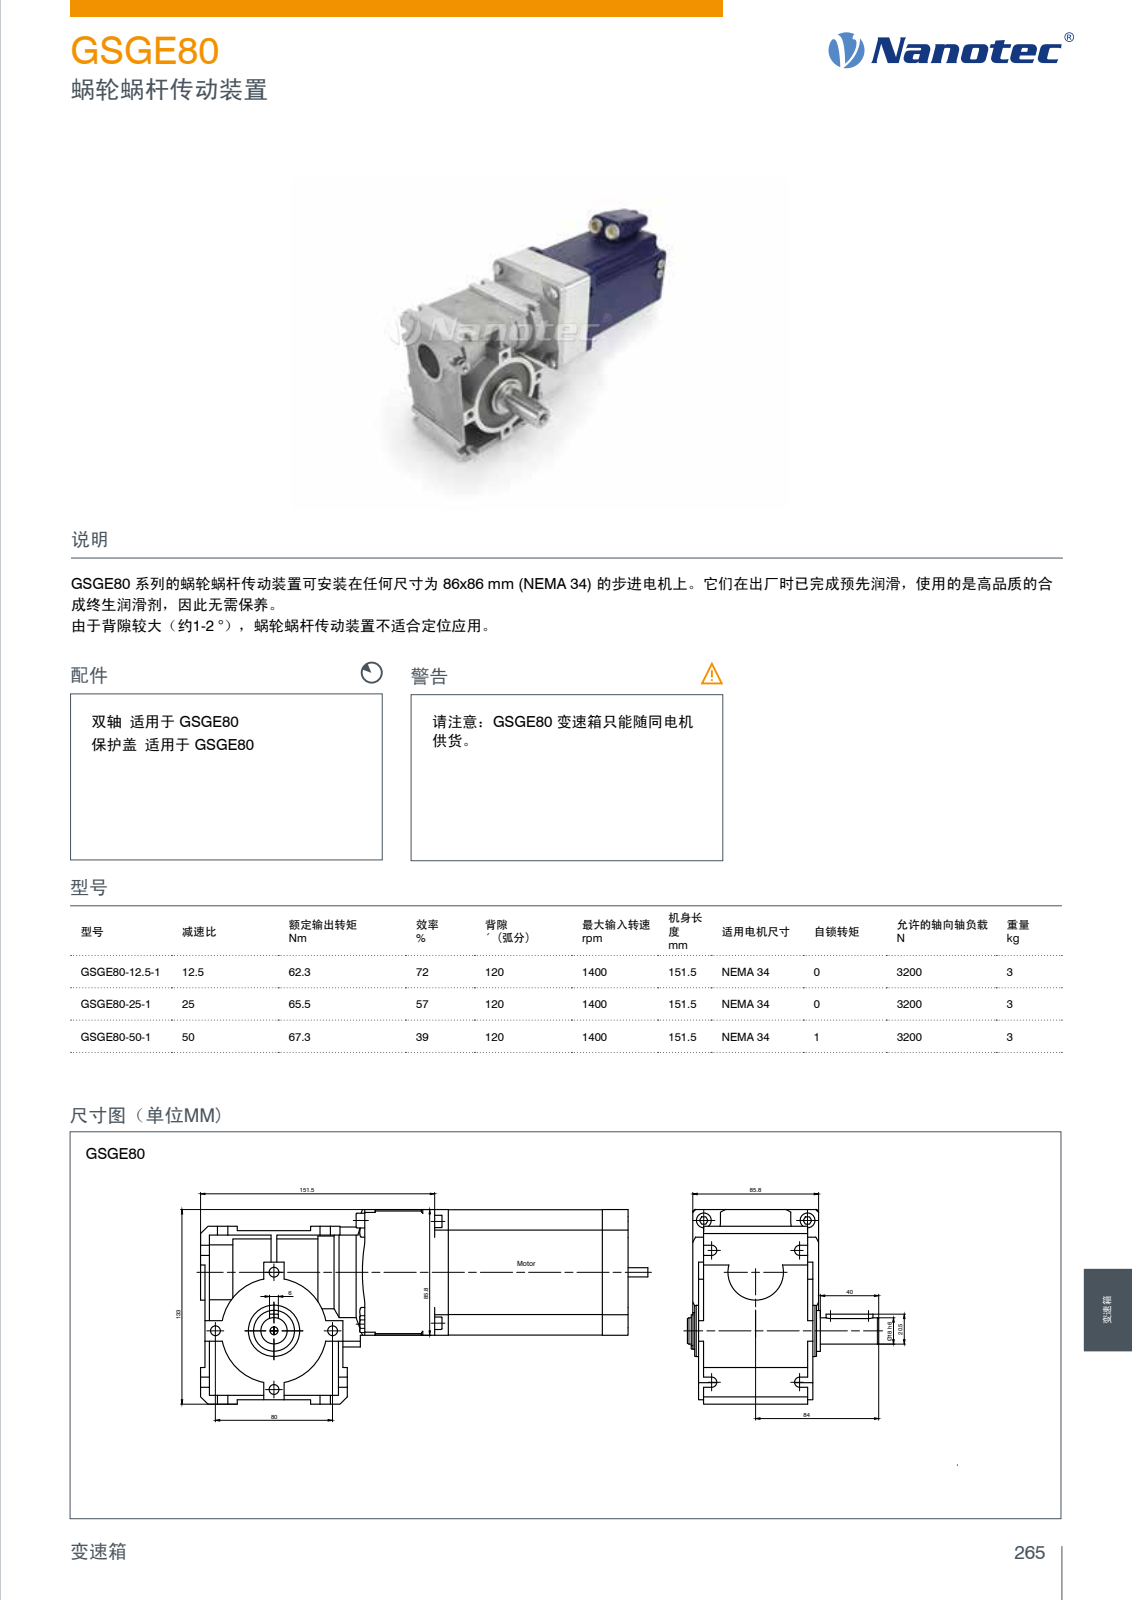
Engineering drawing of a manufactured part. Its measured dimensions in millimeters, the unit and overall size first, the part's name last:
Units: millimetres
Overall size (bounding box): 151.5 × 132.9 × 130.5
Round holes (diameter × count): ⌀4.13 ×4, ⌀6.6 ×4, ⌀2 ×2, ⌀4.92 ×1, ⌀55 ×1, ⌀70 ×1, ⌀73 ×1, ⌀80 ×1
Round bosses / shafts (diameter × count): ⌀8.7 ×4, ⌀79.95 ×1, ⌀50 ×1, ⌀46 ×1, ⌀38 ×1, ⌀35 ×1, ⌀28 ×1, ⌀25 ×1
Partial cylindrical surfaces — rounded edges, fillets, slot ends (radius × count): R3.5 ×8, R5.5 ×4, R10 ×4, R3 ×2, R4 ×2, R10.15 ×1, R11.65 ×1, R31 ×1
Main face-to-face distances: 3, 6, 115.5, 112.5, 39.9, 42, 94, 3.9, 81.9, 85.8
Hole centre spacings: 40, 56.57, 10.39, 30.66, 49.14, 49.15, 49.76, 69.5
Volume: 807 717 mm³ · Surface area: 137 615 mm²
Bodies: 1 solid, 328 faces (202 planar, 78 cylindrical, 48 other)
Part name (STEP PRODUCT): GSGE80_Shrinkwrap_1
STEP written by: Autodesk Inventor 2019 (AUTOMOTIVE_DESIGN)
